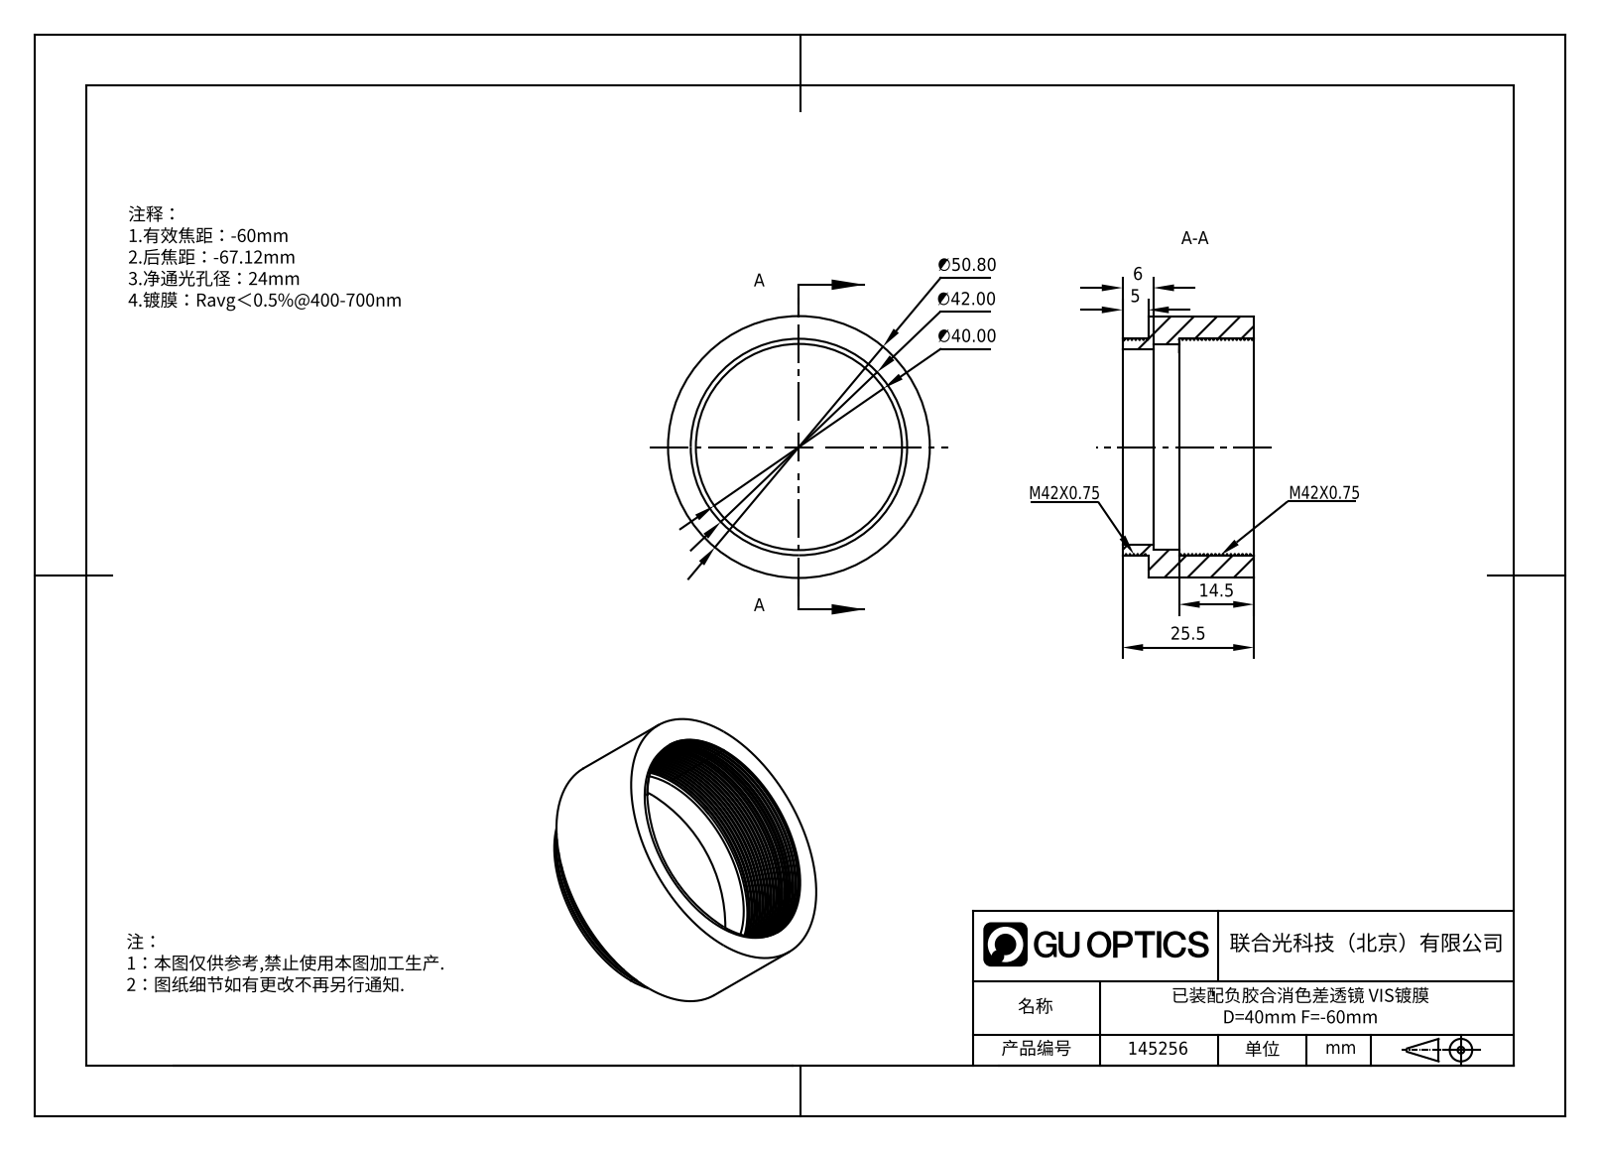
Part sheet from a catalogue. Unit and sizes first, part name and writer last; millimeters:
Units: millimetres
Overall size (bounding box): 50.8 × 50.8 × 25.5
Round holes (diameter × count): ⌀38 ×1, ⌀40 ×1, ⌀42 ×1
Round bosses / shafts (diameter × count): ⌀50.8 ×1
Main face-to-face distances: 1, 1.01, 20.5, 19.5, 19.49, 5, 6, 6.01, 25.5, 11
Volume: 15 356 mm³ · Surface area: 11 919 mm²
Bodies: 1 solid, 79 faces (9 planar, 63 cylindrical, 7 other)
Part name (STEP PRODUCT): APD-ML40-063-VIS-B
STEP written by: SolidWorks 2023 (CONFIG_CONTROL_DESIGN)
